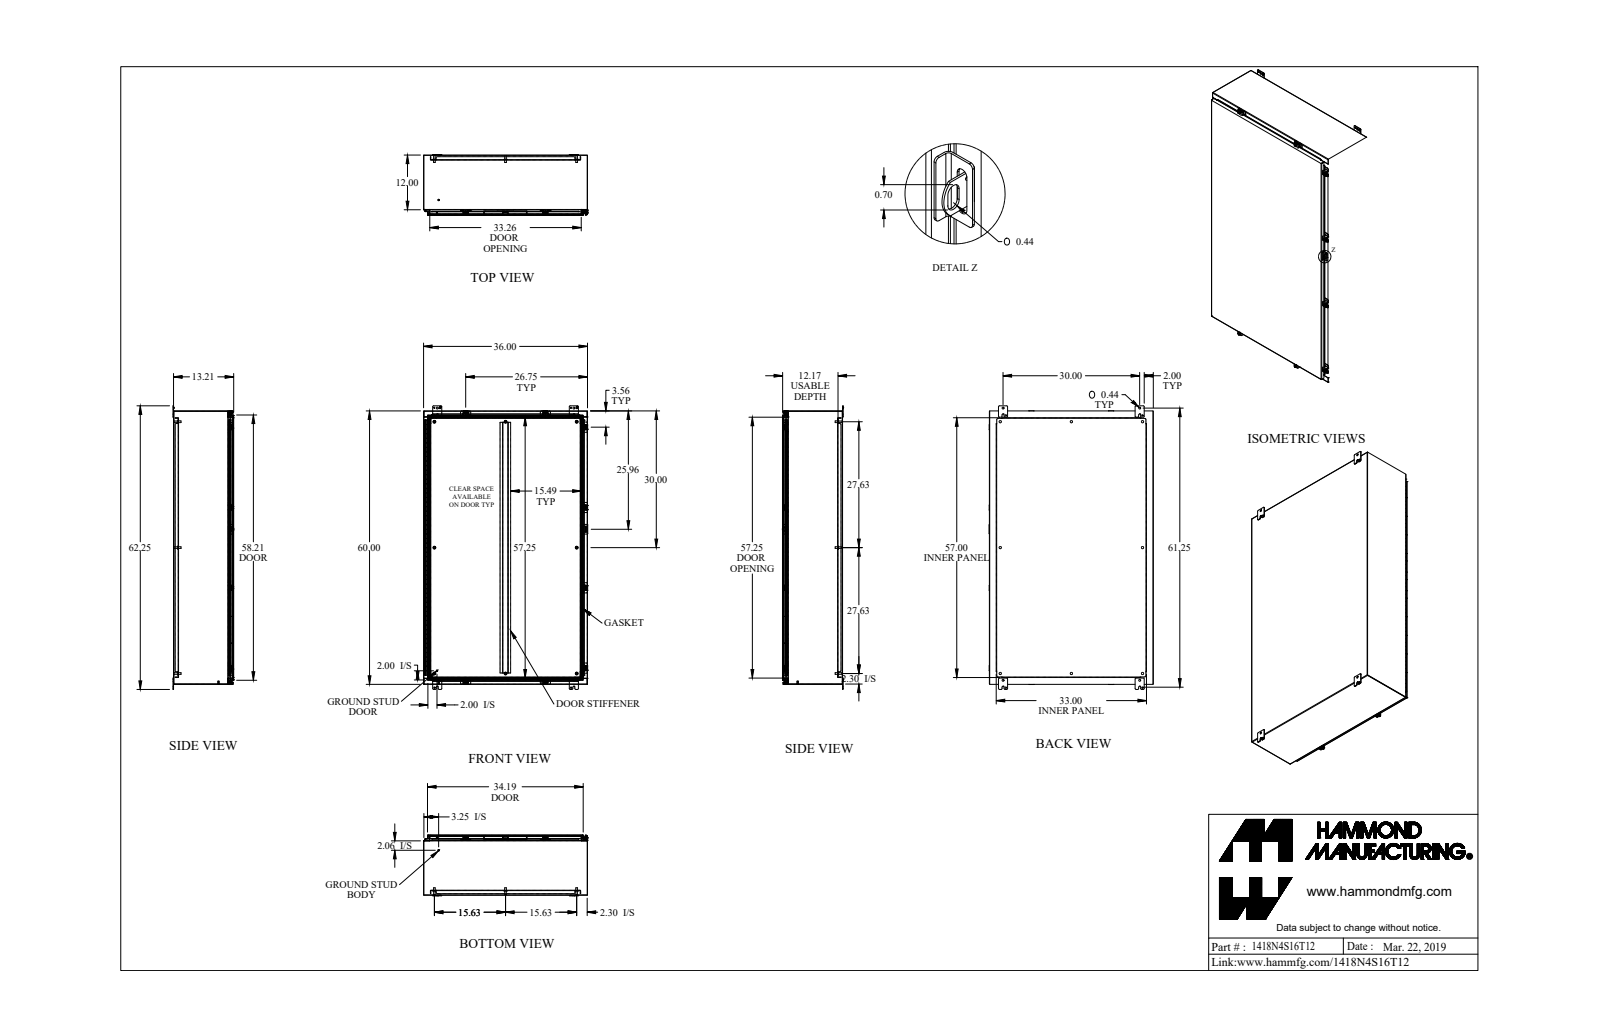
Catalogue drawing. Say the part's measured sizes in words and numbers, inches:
The part is named "1418N4S16T12_Default". Its 3-D file was written by "SolidWorks 2019 (CONFIG_CONTROL_DESIGN)". It is 58 solids with 2147 faces: 1110 planar, 895 cylindrical and 142 other. Overall it measures 62.25 by 36.063 by 13.375 inches. Its volume is 740.8 cubic inches and its surface area 19 332 square inches. Round holes: 8 of diameter 0.213, 8 of diameter 0.265, 8 of diameter 0.375, 8 of diameter 0.5, 4 of diameter 0.313, 4 of diameter 0.437, 1 of diameter 0.11, 1 of diameter 0.125. Round bosses or shafts: 8 of diameter 0.65, 8 of diameter 0.5, 8 of diameter 0.39, 8 of diameter 0.375, 8 of diameter 0.332, 8 of diameter 0.244, 2 of diameter 0.313, 2 of diameter 0.25. Partial cylindrical surfaces (rounded edges, fillets, slot ends): 44 of radius 0.25, 39 of radius 0.048, 39 of radius 0.143, 30 of radius 0.188, 22 of radius 0.036, 22 of radius 0.108, 16 of radius 0.141, 14 of radius 0.125. The main face-to-face distances are 0.072, 13.066, 13.138, 0.072, 0.095, 13.138, 13.21, 0.937, 1.009, 12.201. The hole center spacings are 9.004, 30, 1.736, 31.25, 31.738, 55.25, 59.75, 66.859.
